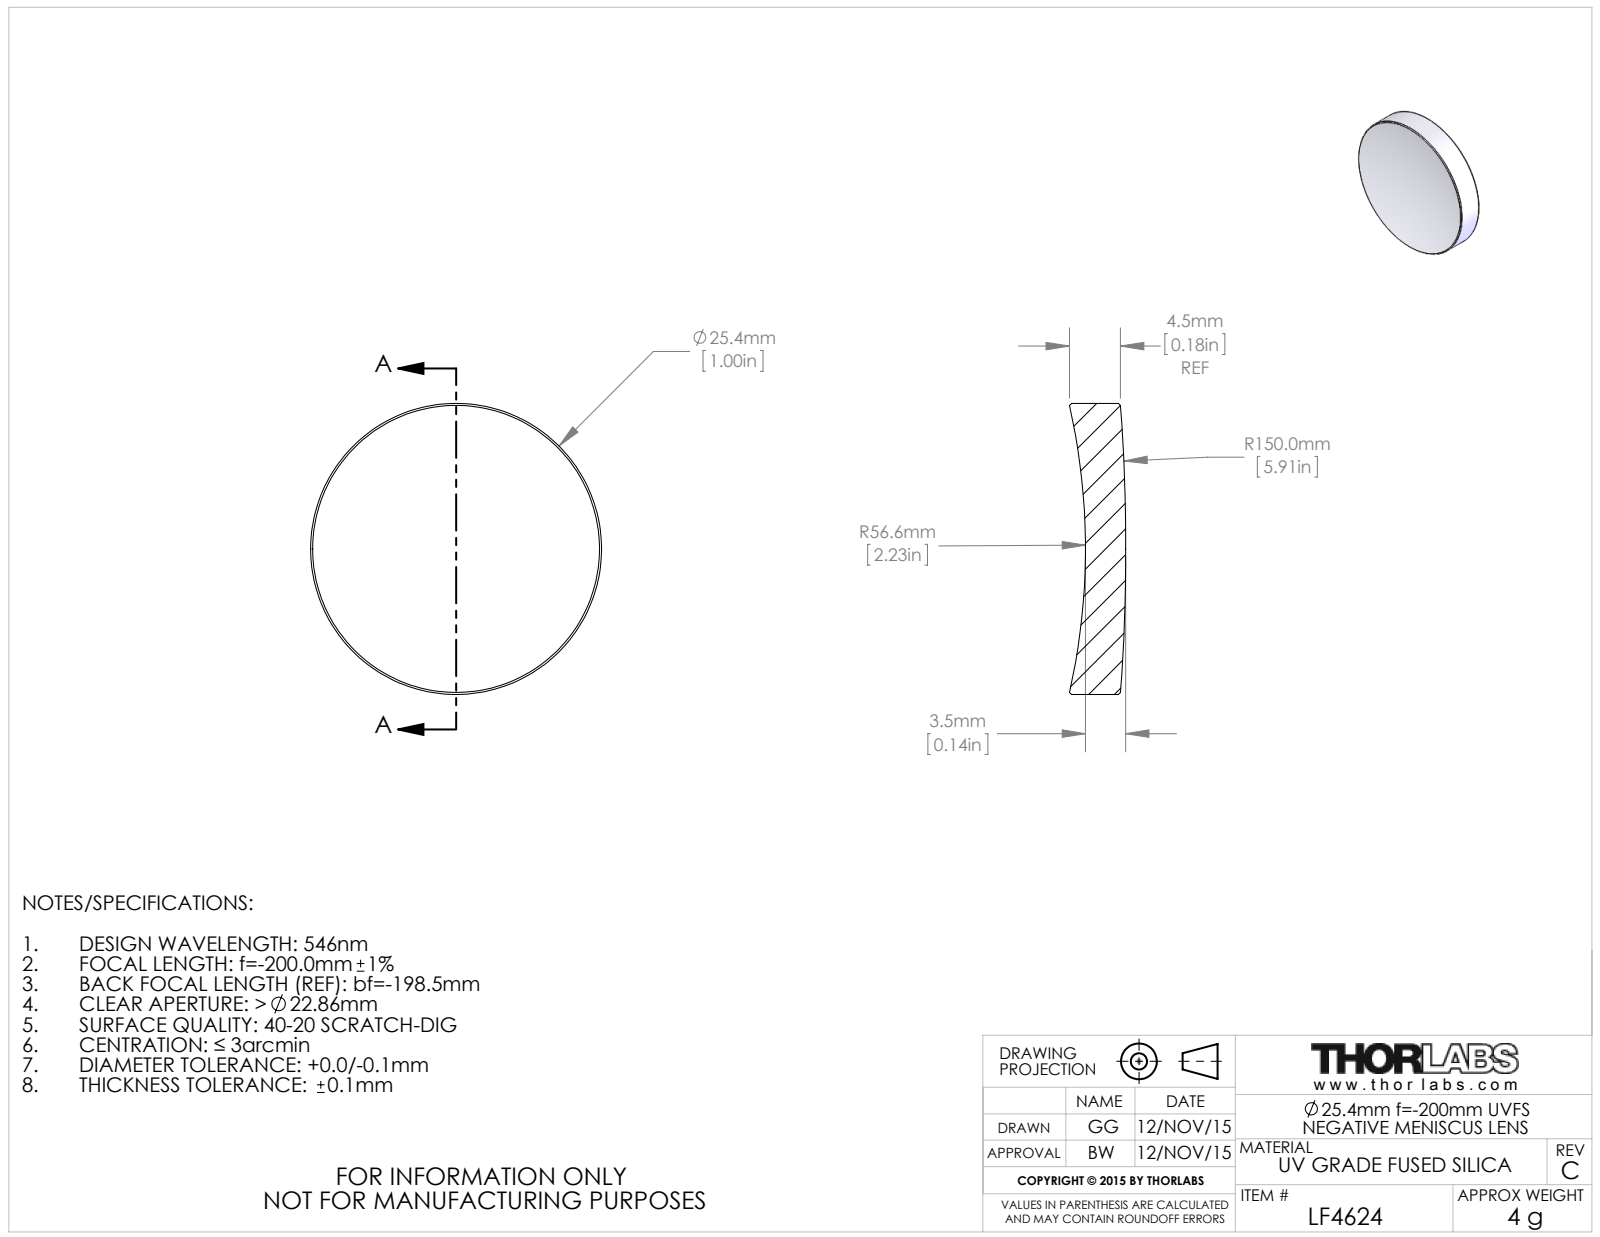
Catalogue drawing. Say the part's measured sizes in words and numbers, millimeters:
The part is named "4220-E0W". Its 3-D file was written by "SolidWorks 2014 (CONFIG_CONTROL_DESIGN)". It is 1 solid with 10 faces: 0 planar, 2 cylindrical and 8 other. Overall it measures 25.4 by 25.4 by 4.9 millimeters. Its volume is 2 030 cubic millimeters and its surface area 1 359 square millimeters. Round bosses or shafts: 1 of diameter 25.4.
